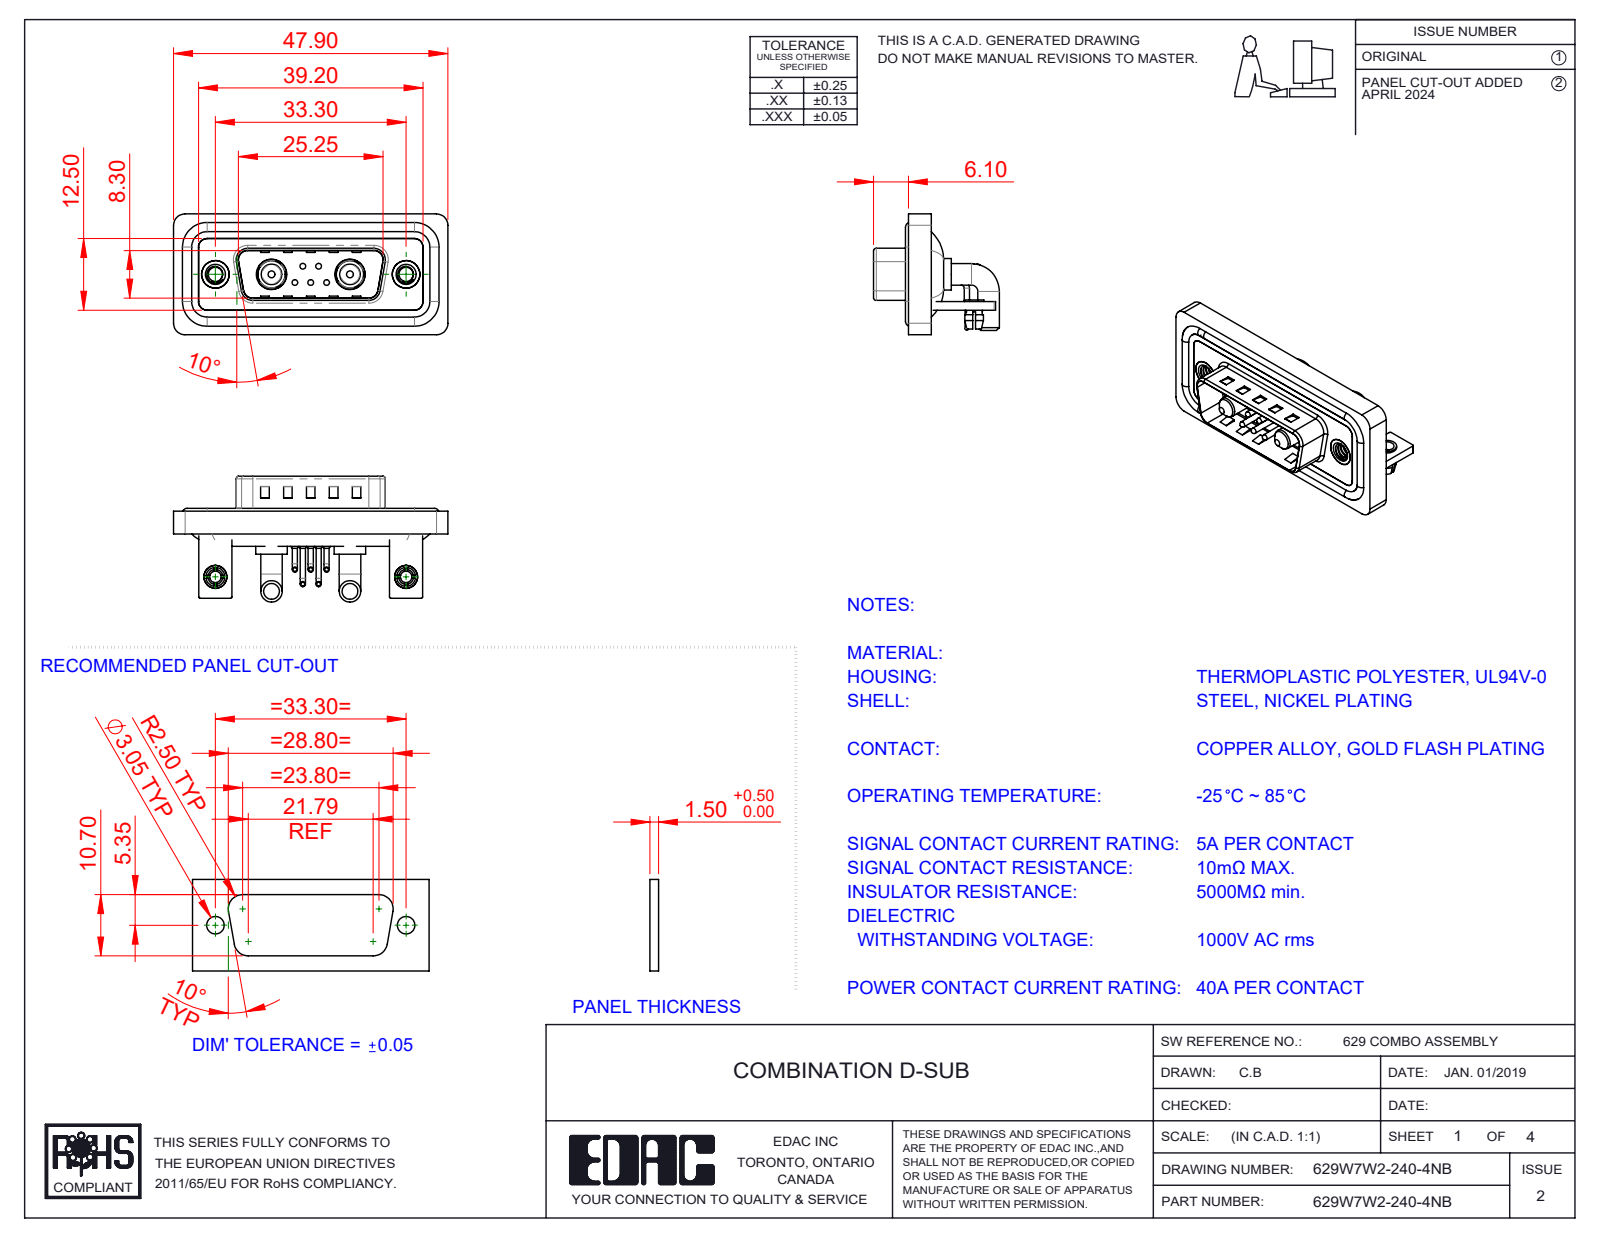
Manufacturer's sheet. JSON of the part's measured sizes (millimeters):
{"part_name": "629Combo Contact Row 2; 629W7W2-140-4NB; 629Combo Stabilizer Bracket; 629Combo Board Lock (+7 more)", "step_written_by": "SolidWorks 2023 (CONFIG_CONTROL_DESIGN)", "units": "millimeters", "bodies": {"solids": 20, "faces": 1213, "planar": 585, "cylindrical": 456, "other": 172}, "overall_size": [47.9, 21.98, 21.1], "volume_mm3": 6135, "surface_area_mm2": 10027, "round_holes": [[2, 7], [0.75, 5], [1.6, 5], [2.5, 4], [3.2, 2], [4, 2], [4.8, 2], [4.85, 2], [5, 2], [5.3, 2]], "round_bosses_or_shafts": [[0.9, 10], [1.5, 5], [1, 5], [0.65, 5], [3.75, 4], [1.6, 4], [5.5, 2], [5.2, 2]], "partial_cylinders_radius": [[2, 21], [1.5, 18], [0.25, 16], [0.5, 9], [1.6, 8], [1.01, 5], [0.6, 4], [0.65, 4]], "face_to_face_distances": [0.4, 1.5, 0.8, 2.9, 2.1, 1.1, 1.6, 1.2, 3.7, 4.5], "hole_center_spacings": [3.16, 2.77, 9.8, 23.5, 33.3, 4.31, 4.33, 5.03]}
